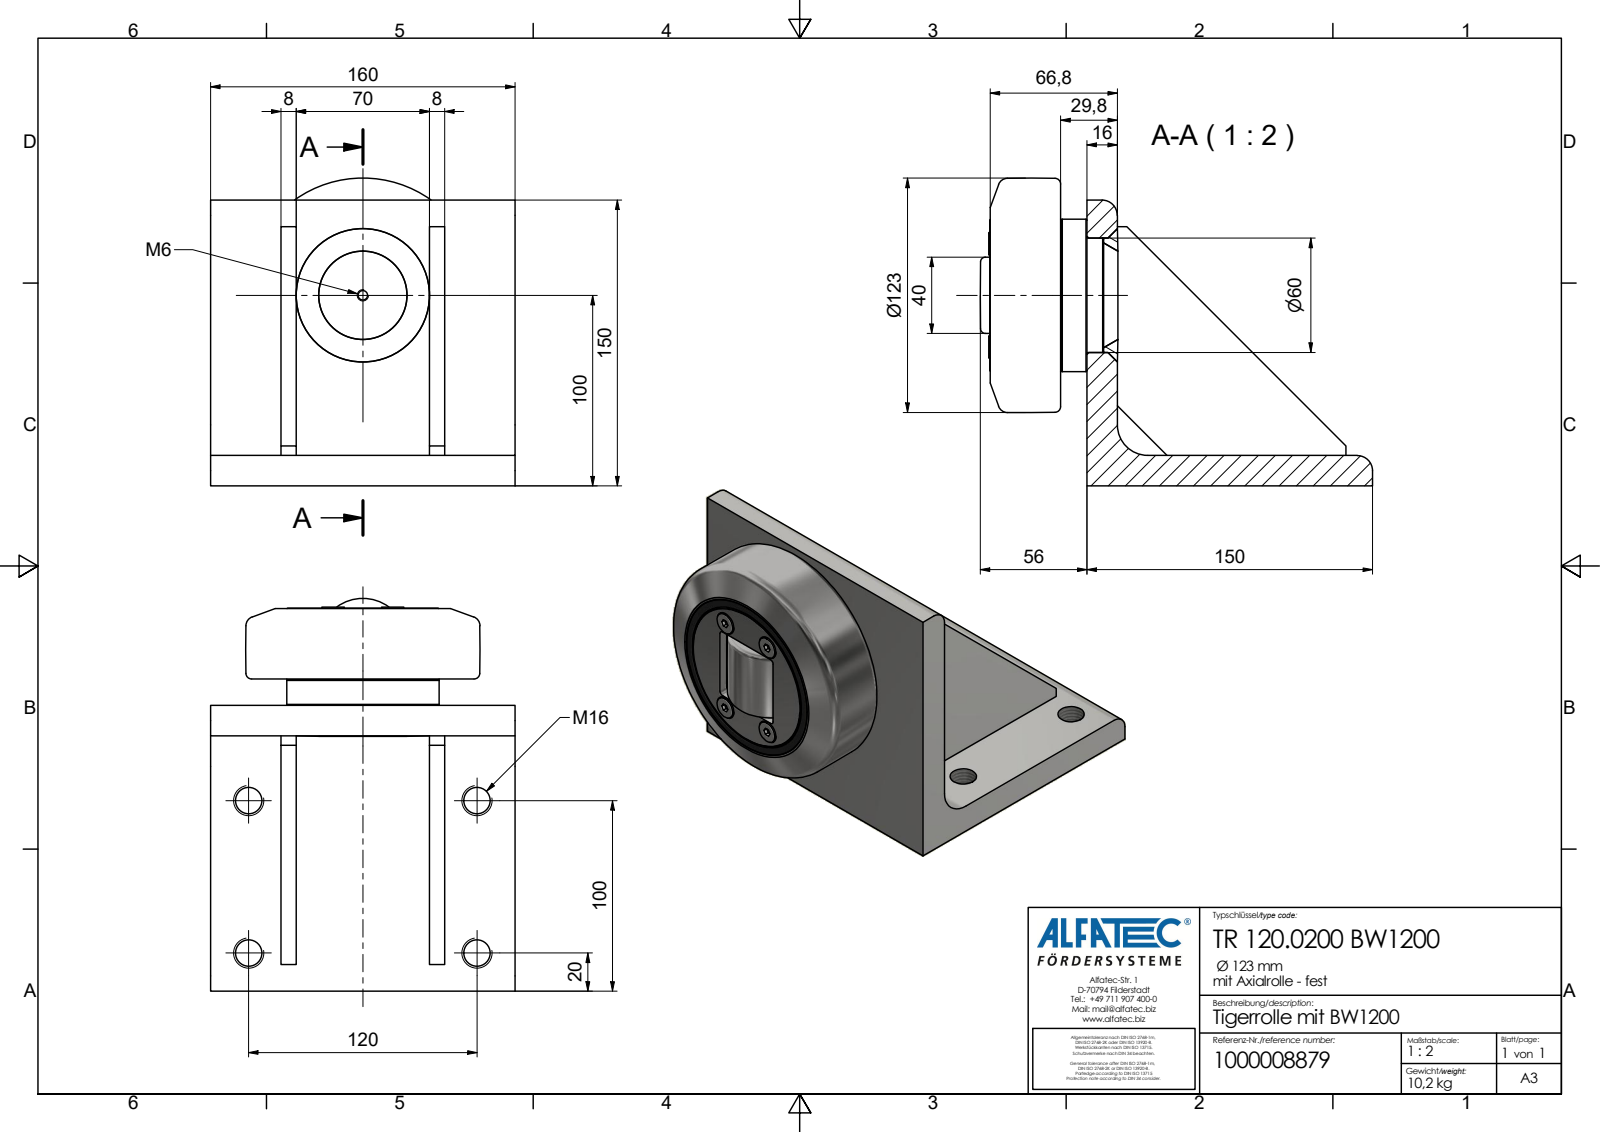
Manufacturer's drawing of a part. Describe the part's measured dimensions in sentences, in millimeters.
The part is named "TR 120.0200 BW1200_Kontur". Its 3-D file was written by "Autodesk Inventor 2020 (AP242_MANAGED_MODEL_BASED_3D_ENGINEERING_MIM_LF)". It is 1 solid with 93 faces: 64 planar, 14 cylindrical and 15 other. Overall it measures 206 by 161.5 by 160 millimeters. Its volume is 1 338 000 cubic millimeters and its surface area 164 131 square millimeters. Round holes: 4 of diameter 13.84, 1 of diameter 4.92. Round bosses or shafts: 4 of diameter 11.7, 1 of diameter 80. Partial cylindrical surfaces (rounded edges, fillets, slot ends): 2 of radius 8, 1 of radius 16. The main face-to-face distances are 16, 8, 78, 37, 45, 115, 123, 70, 86, 29.8. The hole center spacings are 80, 120, 144.22.
